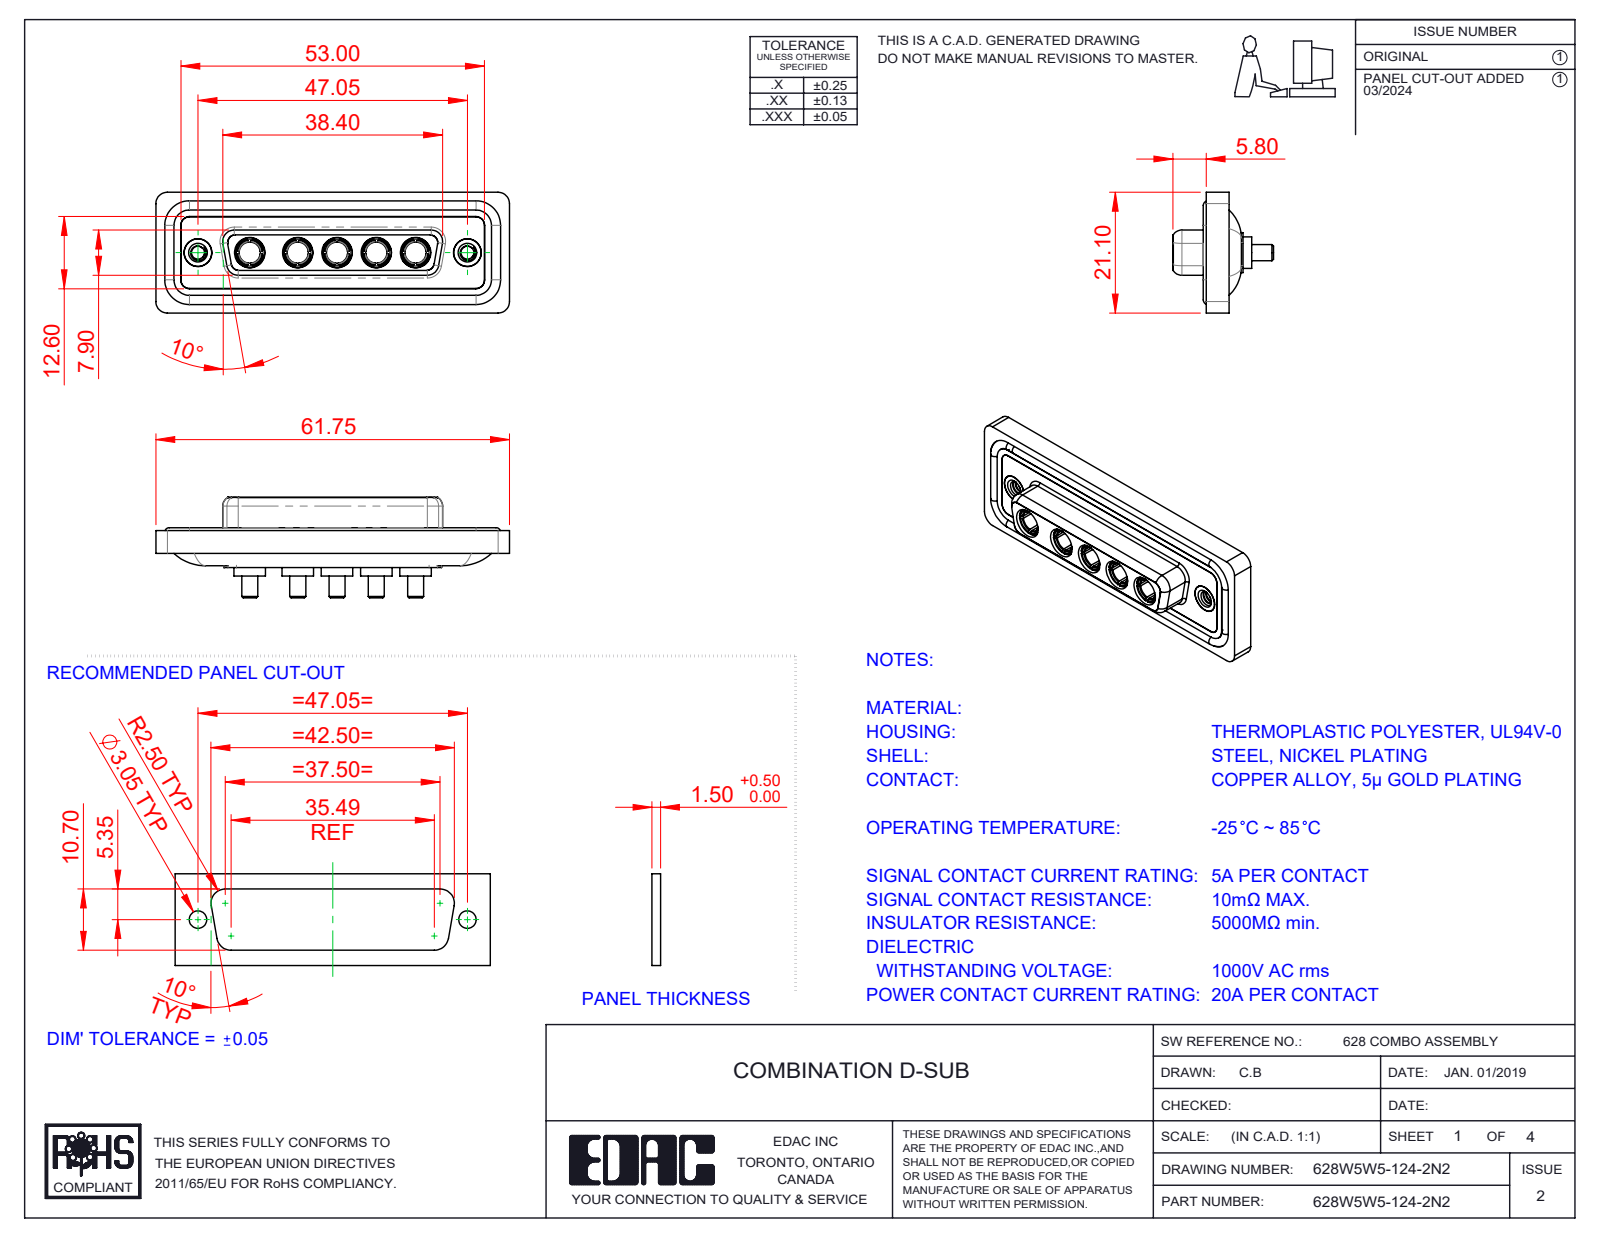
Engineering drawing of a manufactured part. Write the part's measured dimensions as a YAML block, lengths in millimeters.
part_name: "628W5W5-124-2N2; 628Combo Housing_5W5; 628Combo Threaded Rivet_2; Power Socket_20A S (+3 more)"
step_written_by: "SolidWorks 2023 (CONFIG_CONTROL_DESIGN)"
units: millimeters
bodies: {solids: 17, faces: 756, planar: 250, cylindrical: 303, other: 203}
overall_size: [61.75, 21.1, 17.55]
volume: 8172
surface_area: 13415
round_holes:
  - {diameter: 4.85, count: 7}
  - {diameter: 3.7, count: 5}
  - {diameter: 5.3, count: 5}
  - {diameter: 2.26, count: 2}
  - {diameter: 4, count: 2}
  - {diameter: 4.05, count: 2}
  - {diameter: 5, count: 2}
round_bosses_or_shafts:
  - {diameter: 5.5, count: 5}
  - {diameter: 5.2, count: 5}
  - {diameter: 4.96, count: 5}
  - {diameter: 4.75, count: 5}
  - {diameter: 3.75, count: 5}
  - {diameter: 2.8, count: 5}
  - {diameter: 1.6, count: 4}
  - {diameter: 4.95, count: 2}
partial_cylinders:
  - {radius: 1.5, count: 22}
  - {radius: 2, count: 18}
  - {radius: 1.35, count: 8}
  - {radius: 1.6, count: 8}
  - {radius: 2.1, count: 5}
  - {radius: 0.25, count: 4}
  - {radius: 0.5, count: 4}
  - {radius: 0.6, count: 4}
face_to_face_distances: [0.4, 1.8, 7.45, 5.65, 0.5, 7.05, 6.6, 1.6, 1.1, 2.9]
hole_center_spacings: [6.86, 9.04, 13.72, 38.01, 8.39, 15.25, 15.9, 17.43]
